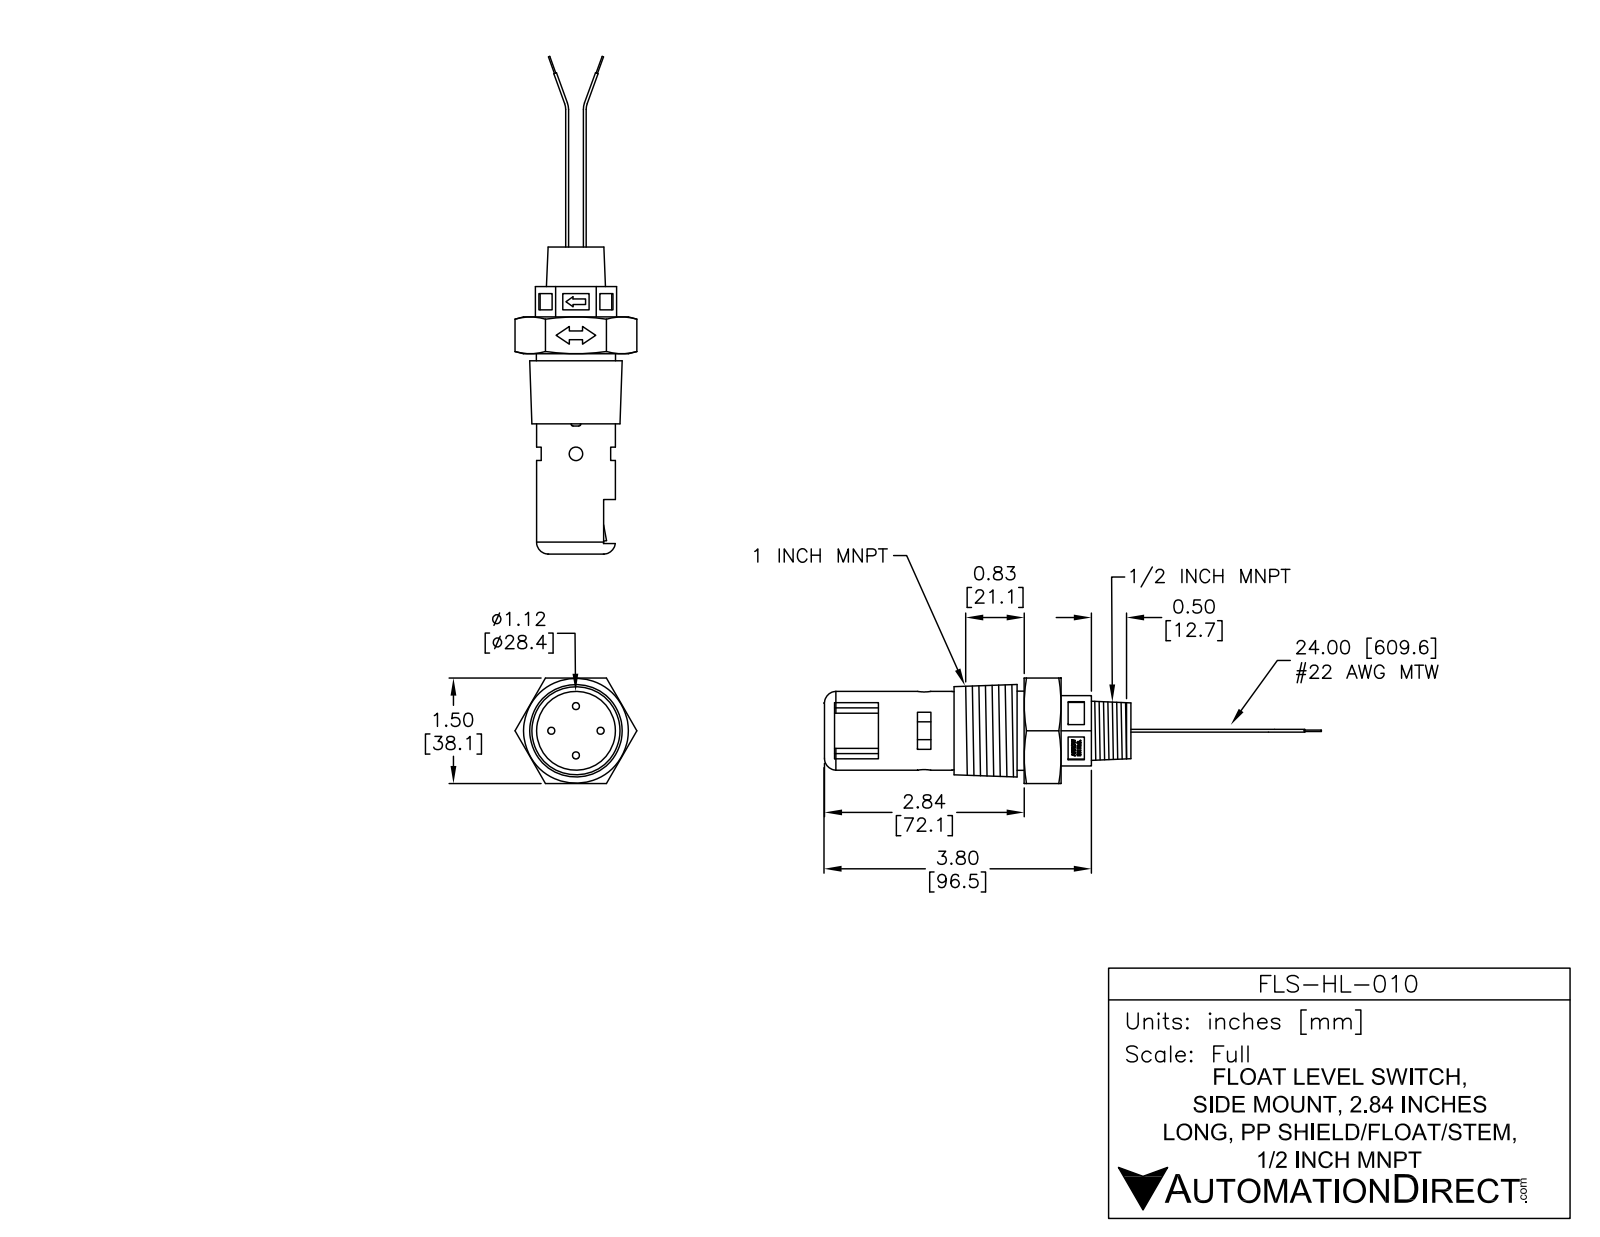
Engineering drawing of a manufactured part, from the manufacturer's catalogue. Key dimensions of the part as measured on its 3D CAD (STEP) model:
Part name (STEP PRODUCT): FLS-HL-010
STEP written by: SolidWorks 2013 (AUTOMOTIVE_DESIGN)
Units: inches
Bodies: 14 solids, 202 faces (131 planar, 59 cylindrical, 12 other)
Overall size (bounding box): 7.142 × 1.732 × 1.5
Volume: 3.252 in³ · Surface area: 37.59 in²
Round holes (diameter × count): ⌀0.1 ×4, ⌀0.19 ×1, ⌀1.02 ×1
Round bosses / shafts (diameter × count): ⌀0.04 ×4, ⌀0.02 ×2, ⌀1.25 ×1, ⌀1.12 ×1
Partial cylindrical surfaces — rounded edges, fillets, slot ends (radius × count): R0.15 ×2
Main face-to-face distances: 0.62, 1.05, 1.52, 0.43, 1.5, 1, 1.95, 0.9, 0.25, 1.25
Hole centre spacings: 0.34, 0.481, 0.68
